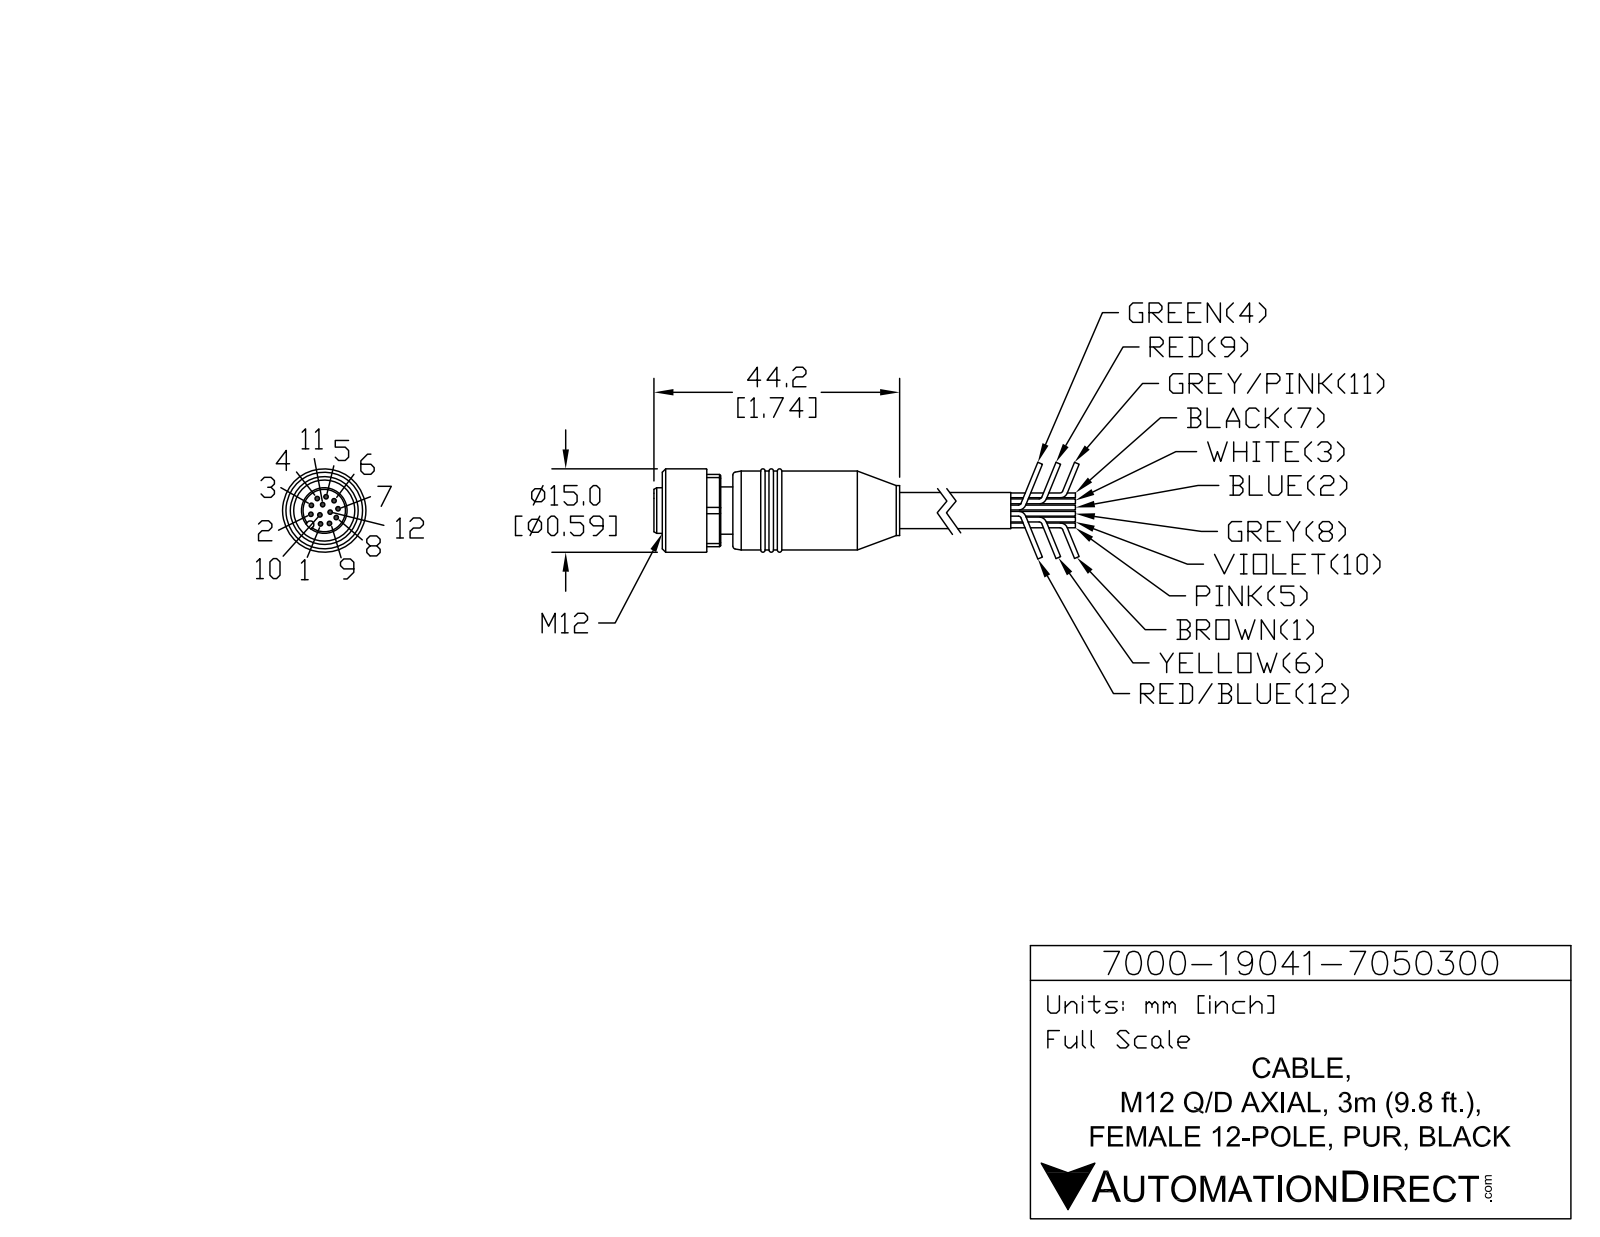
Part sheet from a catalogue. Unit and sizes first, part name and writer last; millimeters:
Units: millimetres
Overall size (bounding box): 64.2 × 15 × 15
Round holes (diameter × count): ⌀0.8 ×12, ⌀11 ×1
Round bosses / shafts (diameter × count): ⌀15 ×1, ⌀14.2 ×1, ⌀9 ×1, ⌀8.5 ×1, ⌀8.2 ×1, ⌀6.5 ×1
Partial cylindrical surfaces — rounded edges, fillets, slot ends (radius × count): R0.65 ×1, R7.2 ×1
Main face-to-face distances: 2.2, 13, 3, 5.2, 9, 12, 14.2, 64.2, 55.2, 52.2
Hole centre spacings: 2.5, 1.61, 4.17, 3.05, 4.84, 4.99, 1.1, 4.61
Volume: 6 619 mm³ · Surface area: 3 428 mm²
Bodies: 1 solid, 115 faces (35 planar, 52 cylindrical, 28 other)
Part name (STEP PRODUCT): 7000-19041-7050300
STEP written by: SolidWorks 2015 (AUTOMOTIVE_DESIGN)
